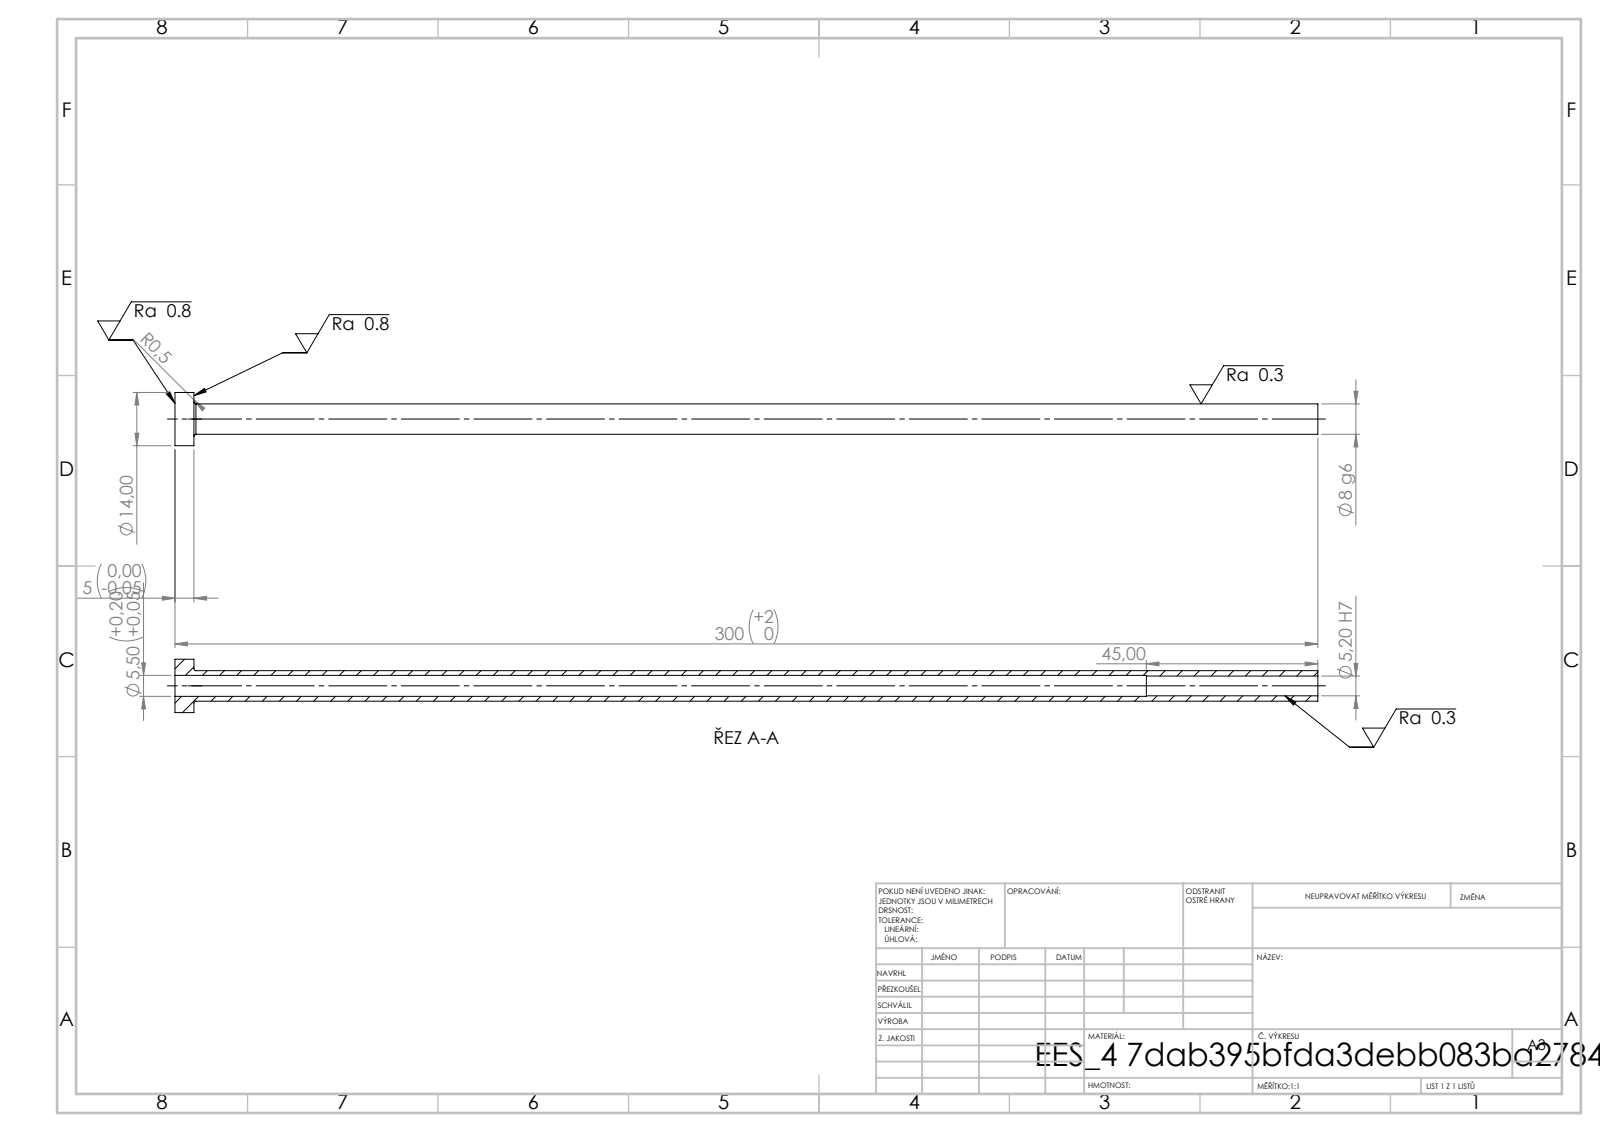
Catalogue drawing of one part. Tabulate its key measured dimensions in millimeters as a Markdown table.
| quantity | value |
| --- | --- |
| STEP written by | SolidWorks 2019 (CONFIG_CONTROL_DESIGN) |
| units | millimeters |
| bodies | 1 solid, 14 faces (4 planar, 8 cylindrical, 2 other) |
| overall size | 300 × 14 × 14 |
| volume | 8 585 mm³ |
| surface area | 13 035 mm² |
| round holes (diameter × count) | 5.2 × 1, 5.5 × 1 |
| round bosses / shafts (diameter × count) | 14 × 1, 8 × 1 |
| main face-to-face distances | 5, 300, 295, 255, 250, 45 |
